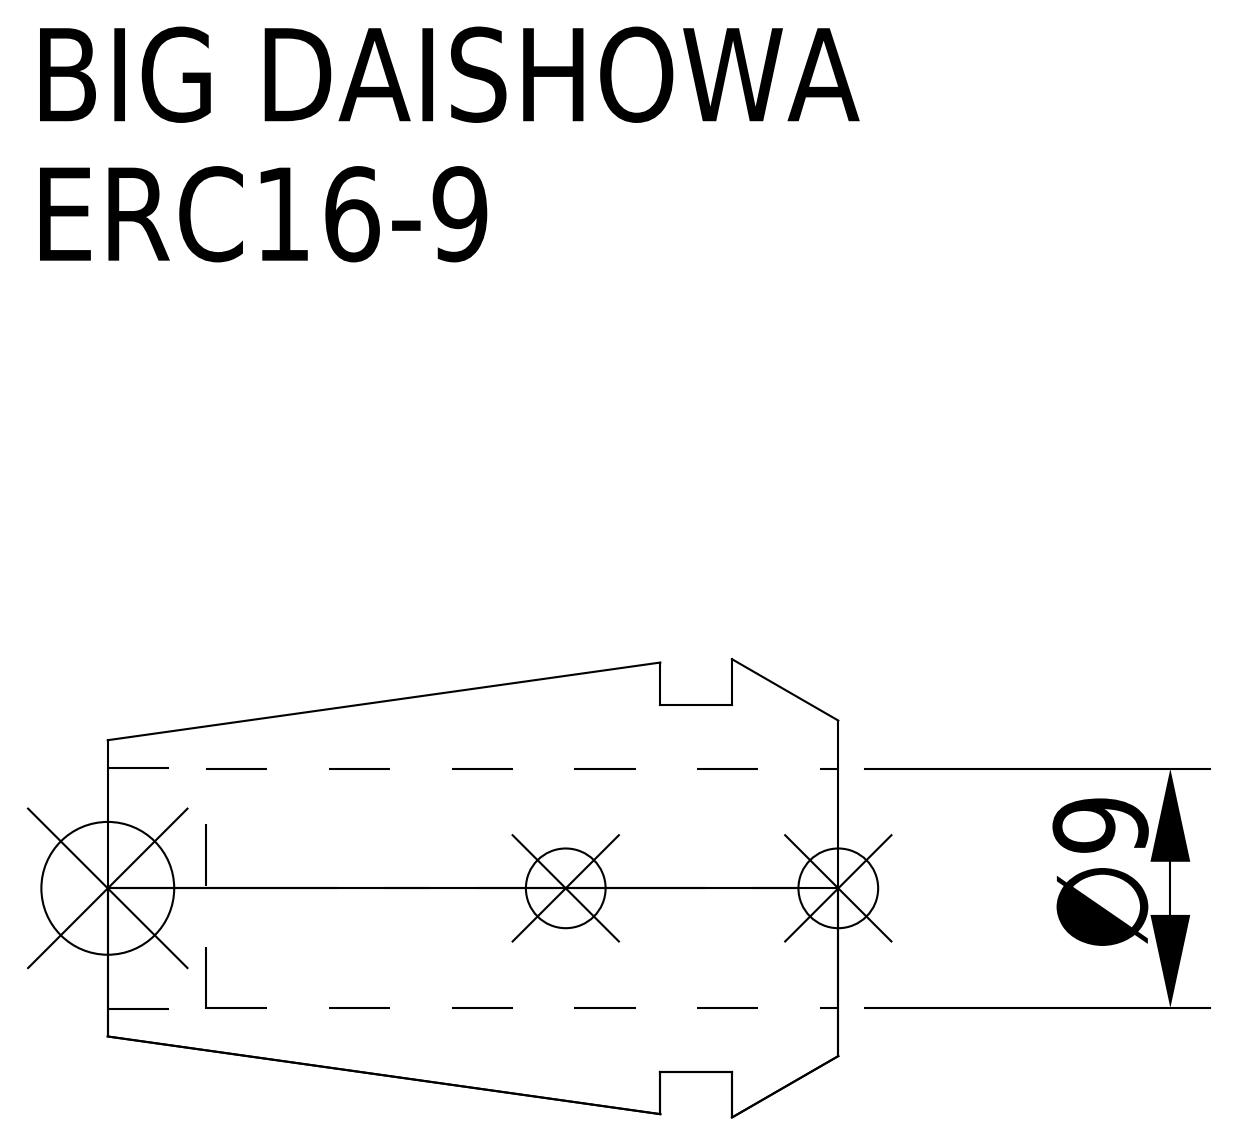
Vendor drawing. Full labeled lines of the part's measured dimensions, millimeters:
Part name (STEP PRODUCT): ERC16-9
STEP written by: CREO PARAMETRIC BY PTC INC, 2016380 (AUTOMOTIVE_DESIGN)
Units: millimetres
Bodies: 1 solid, 15 faces (5 planar, 6 cylindrical, 4 other)
Overall size (bounding box): 27.5 × 17.25 × 17.25
Volume: 2 643 mm³ · Surface area: 2 298 mm²
Round holes (diameter × count): ⌀9 ×1, ⌀9.05 ×1
Round bosses / shafts (diameter × count): ⌀13.8 ×1
Main face-to-face distances: 2.7, 4, 6.7, 27.5, 23.5, 20.8, 23.8, 19.8, 17.1, 3.7
